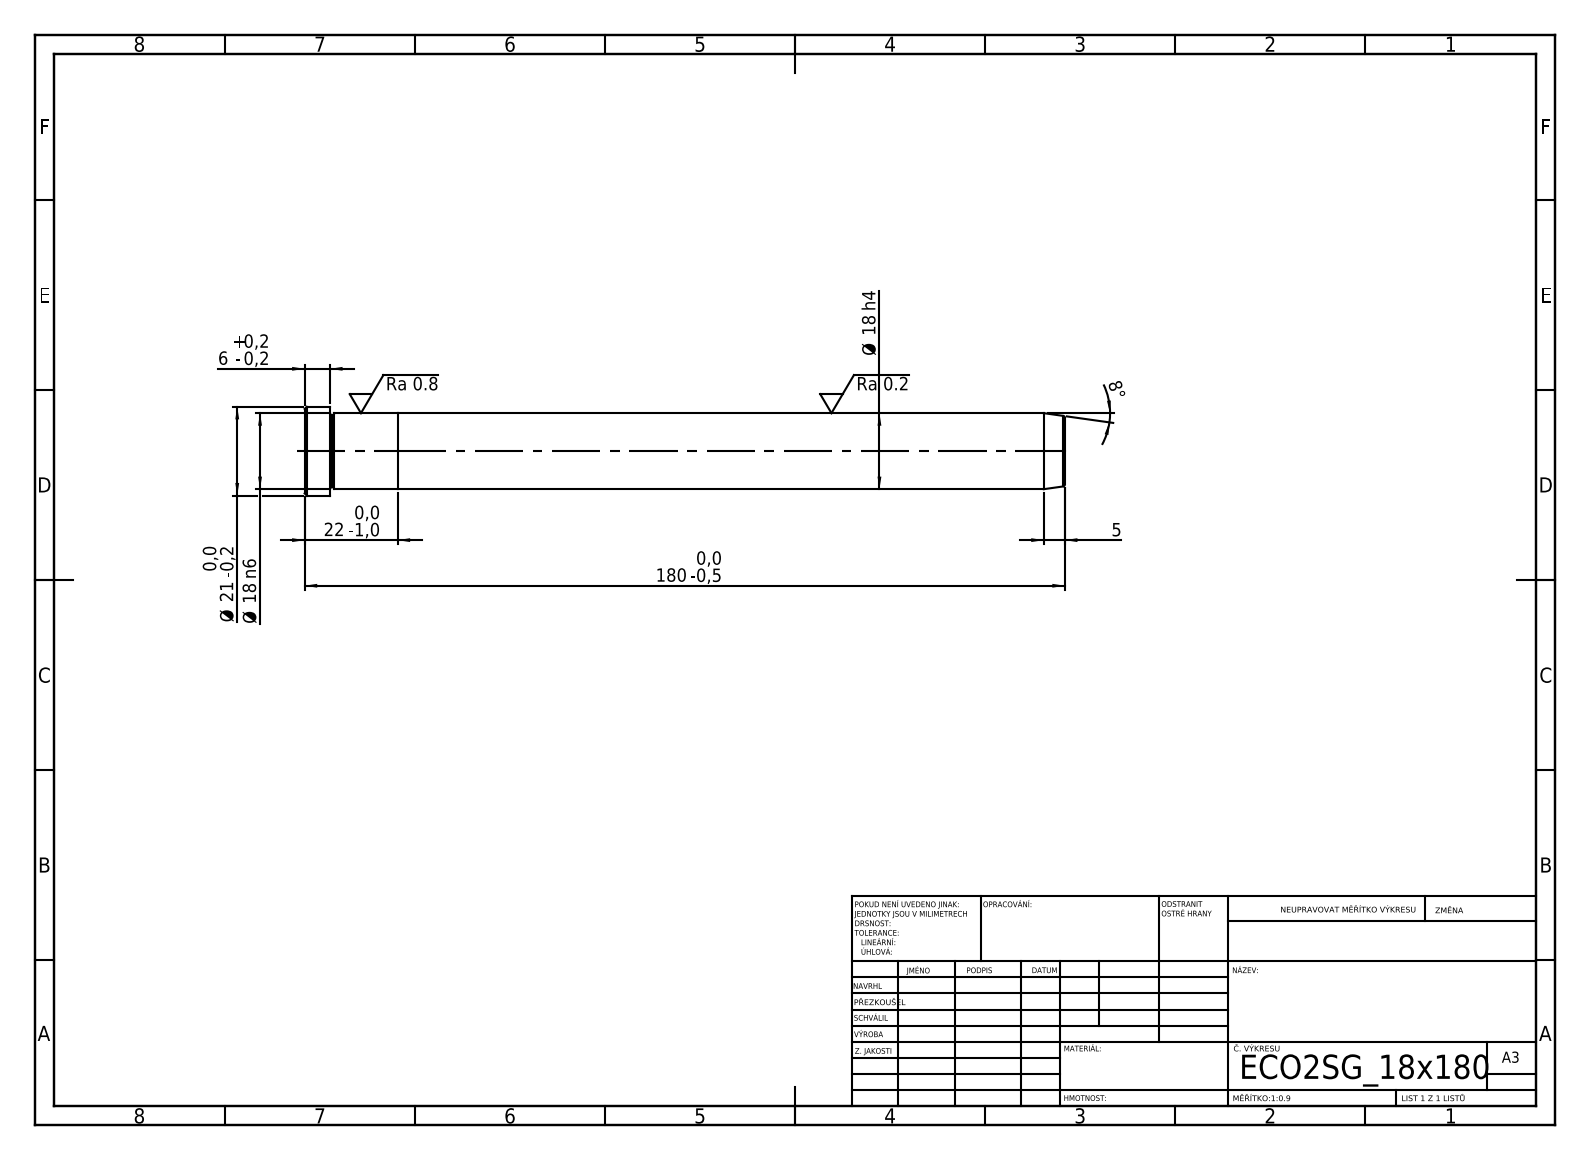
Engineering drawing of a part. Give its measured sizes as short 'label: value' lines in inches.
written by: SolidWorks 2019 (CONFIG_CONTROL_DESIGN)
unit: in
bodies: 2 solids, 21 faces (5 planar, 6 cylindrical, 10 other)
size: 7.087 × 0.827 × 0.827
volume: 2.821 in³; area: 17.66 in²
bosses: 1× ⌀0.827, 1× ⌀0.709
face distances: 0.866, 6.22, 7.087, 6.85, 0.63, 0.236
